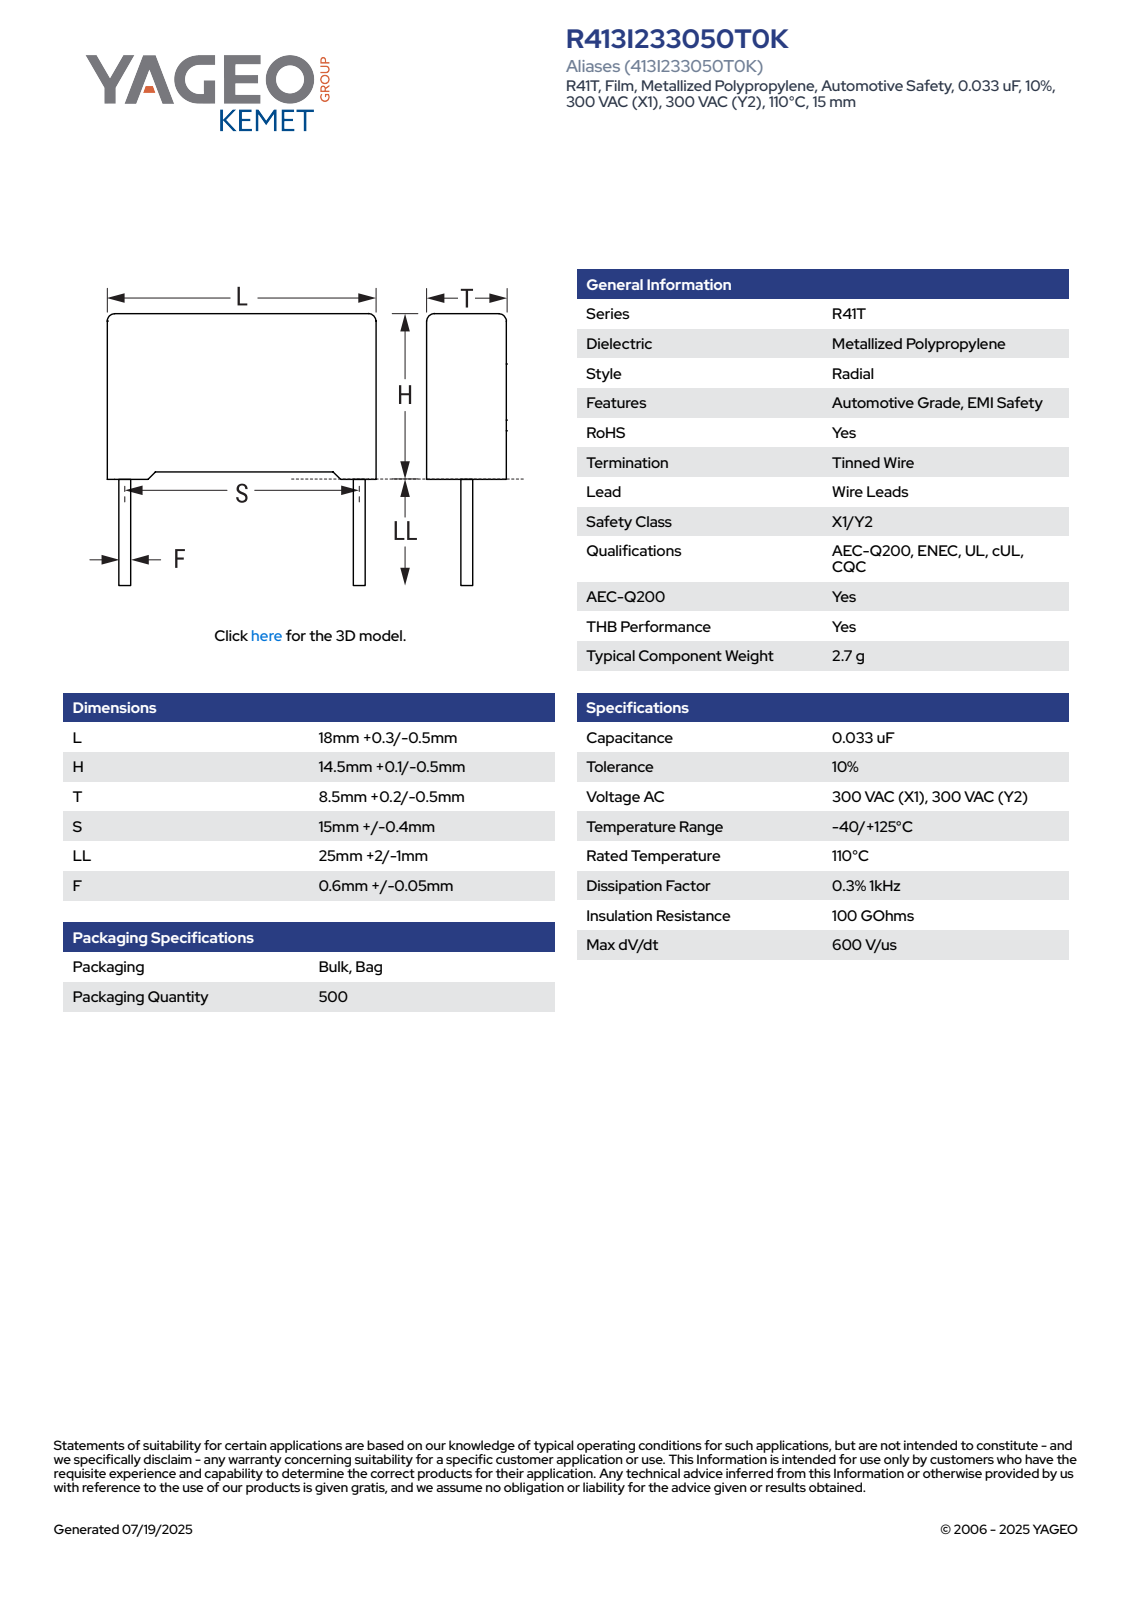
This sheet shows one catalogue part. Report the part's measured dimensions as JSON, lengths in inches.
{"part_name": "CFR_RB2_18X14.5X8.5_L18.3H14.6T8.7S15LL27F0.65", "step_written_by": "SolidWorks 2021 (AUTOMOTIVE_DESIGN)", "units": "inches", "bodies": {"solids": 4, "faces": 85, "planar": 77, "cylindrical": 8, "other": 0}, "overall_size": [1.638, 0.72, 0.343], "volume_in3": 0.137, "surface_area_in2": 1.934, "round_bosses_or_shafts": [[0.026, 2]], "partial_cylinders_radius": [[0.02, 4]], "face_to_face_distances": [0.343, 0.545, 0.72, 0.024, 0.03, 0.575, 0.319, 0.02, 0.555, 0.696]}
